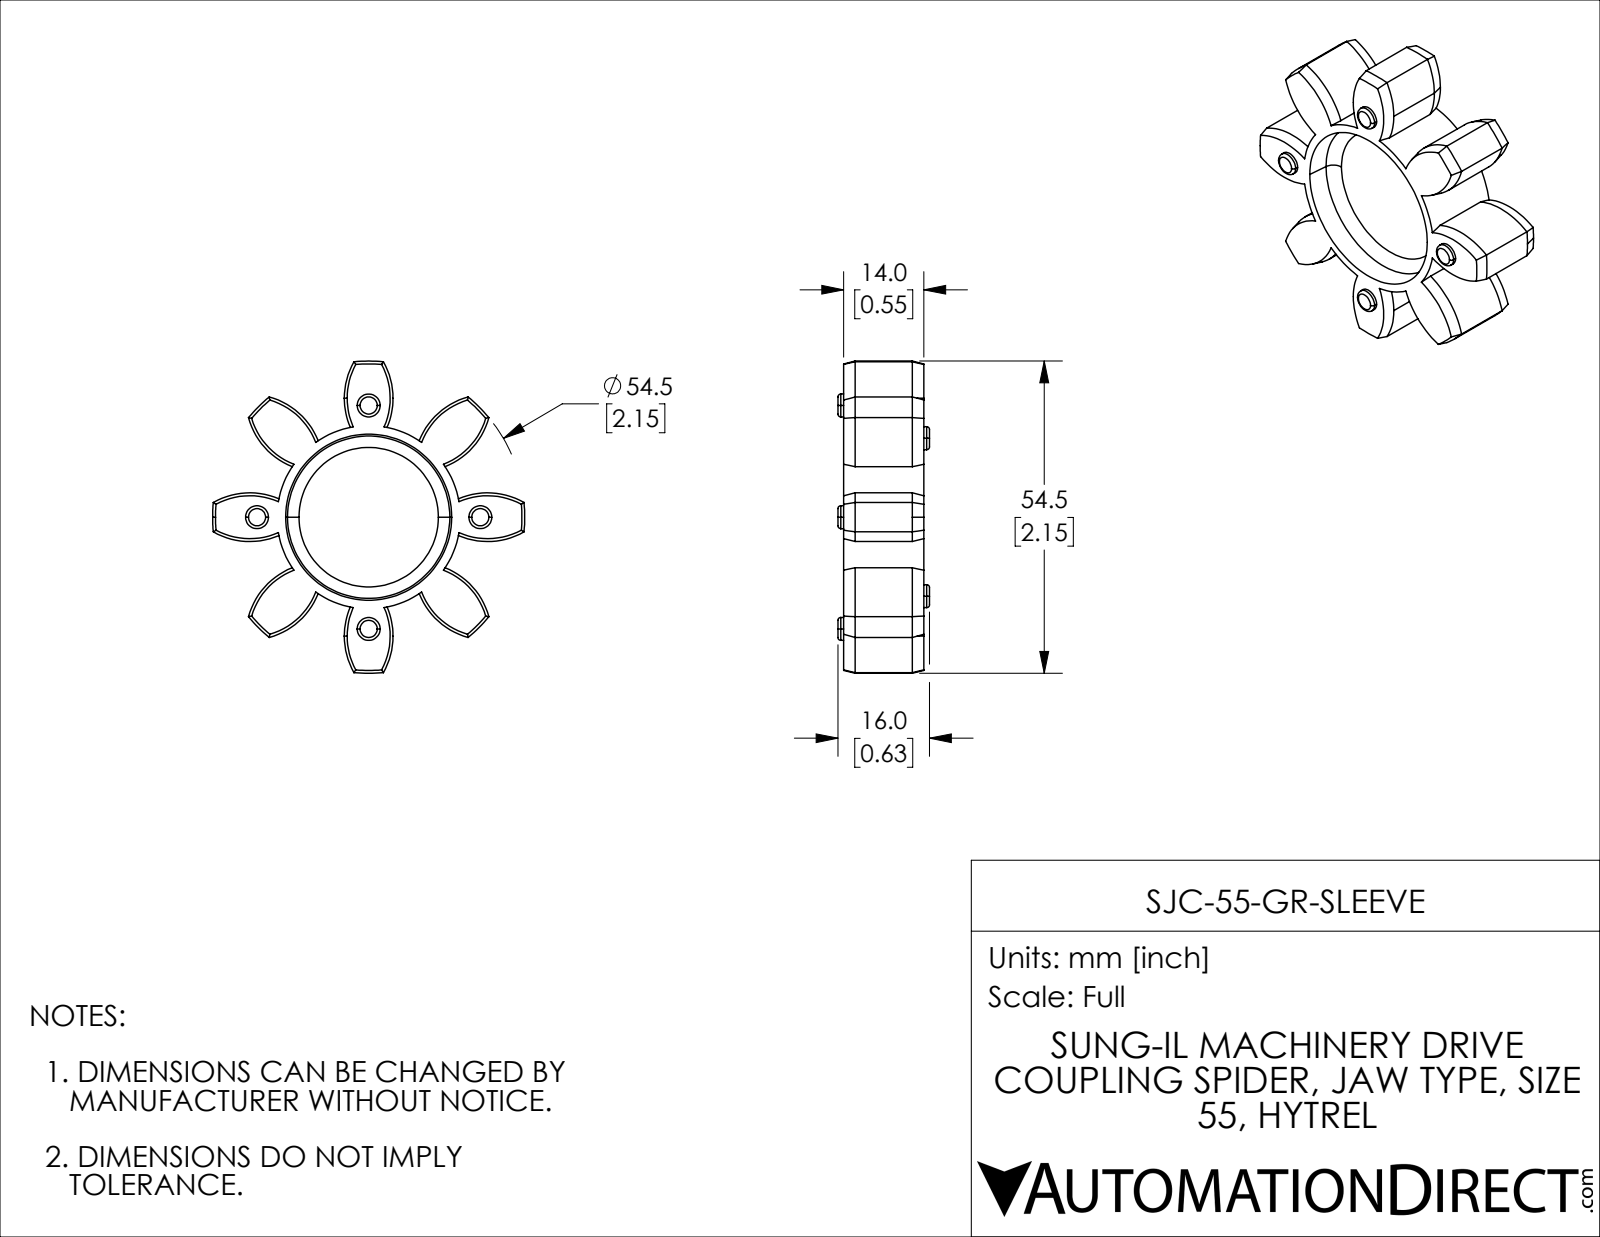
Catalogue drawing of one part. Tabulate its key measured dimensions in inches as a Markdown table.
| quantity | value |
| --- | --- |
| part name | SJC-55-GR-SLEEVE |
| STEP written by | SolidWorks 2021 (CONFIG_CONTROL_DESIGN) |
| units | inches |
| bodies | 1 solid, 141 faces (12 planar, 51 cylindrical, 78 other) |
| overall size | 2.146 × 2.146 × 0.63 |
| volume | 0.845 in³ |
| surface area | 11.7 in² |
| round bosses / shafts (diameter × count) | 0.157 × 8 |
| partial cylindrical surfaces (radius × count) | 0.506 × 8, 0.63 × 1, 1.073 × 1 |
| main face-to-face distances | 0.217, 0.335, 0.551, 0.118, 0.039, 0.256, 0.374, 0.591, 0.63 |
